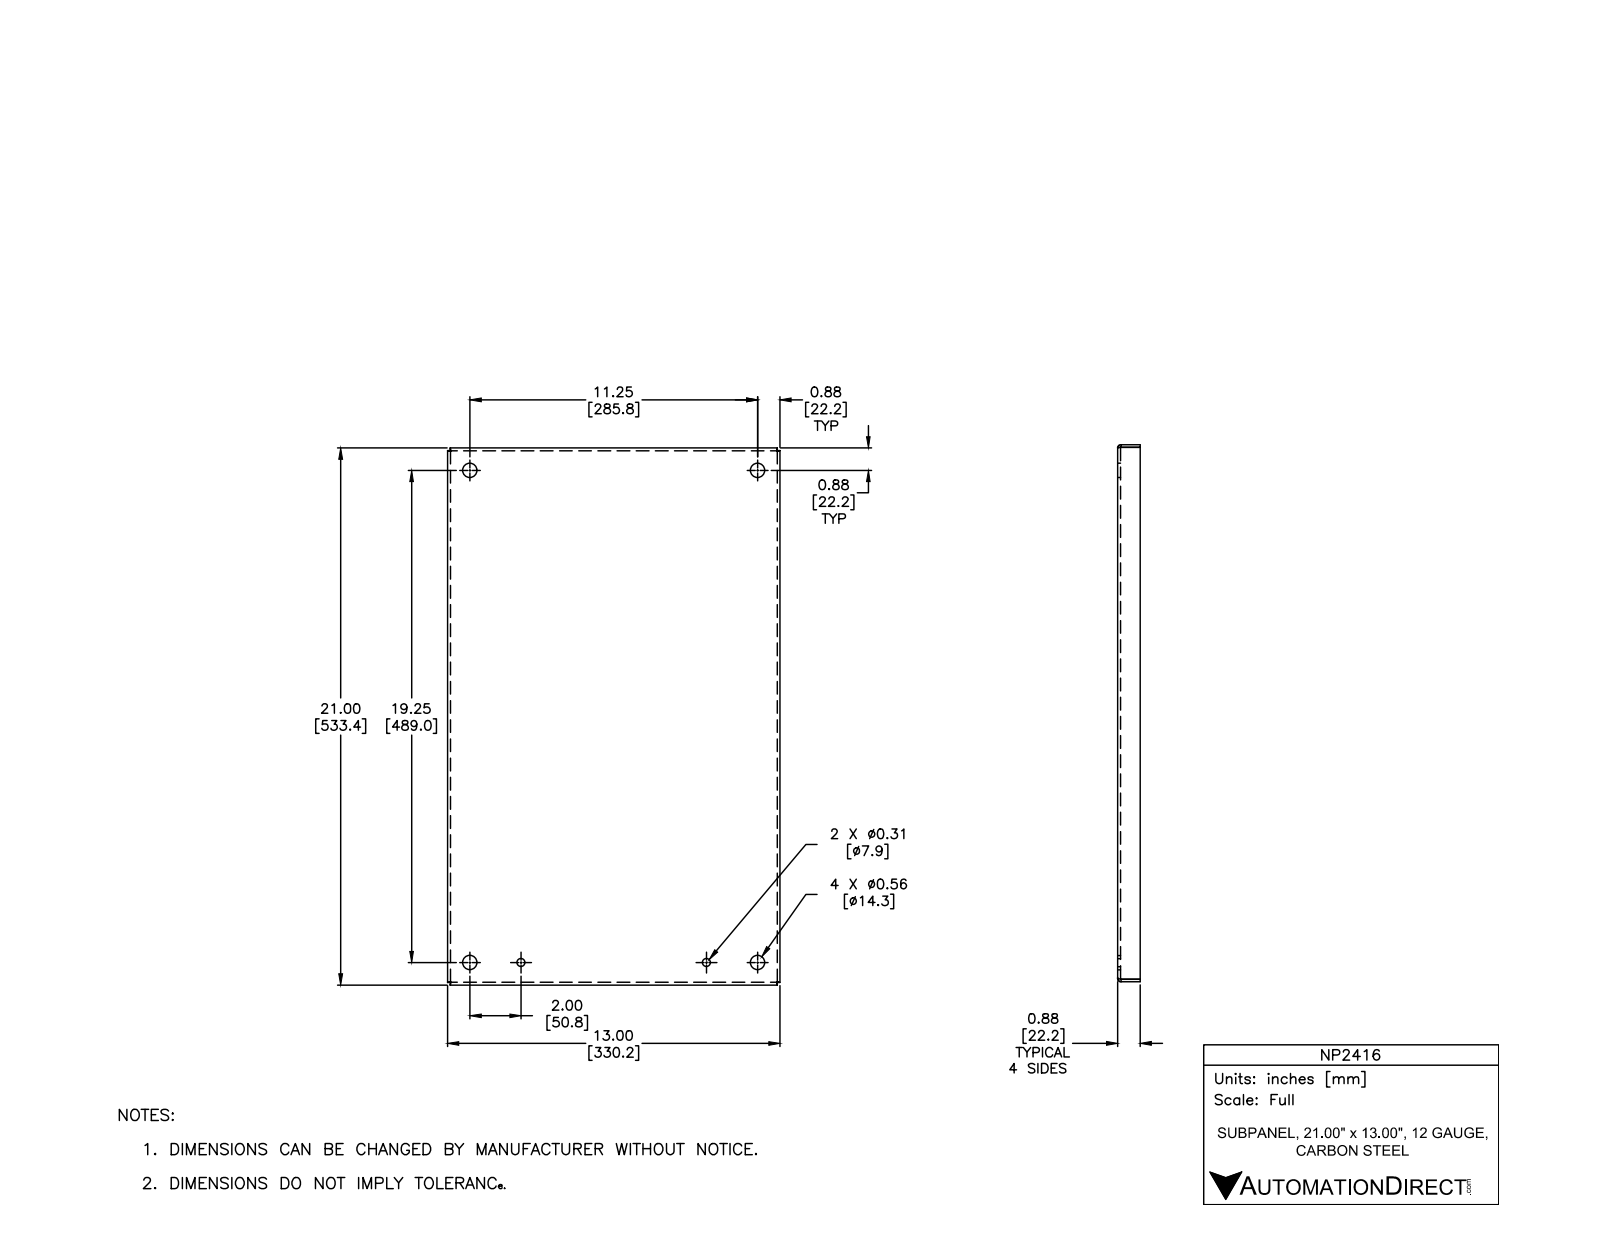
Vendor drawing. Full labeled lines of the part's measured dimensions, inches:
Part name (STEP PRODUCT): NP2416
STEP written by: Autodesk Inventor 2012 (AUTOMOTIVE_DESIGN)
Units: inches
Bodies: 1 solid, 44 faces (22 planar, 14 cylindrical, 8 other)
Overall size (bounding box): 21 × 13 × 0.875
Volume: 30.19 in³ · Surface area: 651.8 in²
Round holes (diameter × count): ⌀0.563 ×4, ⌀0.312 ×2
Partial cylindrical surfaces — rounded edges, fillets, slot ends (radius × count): R0.031 ×4, R0.125 ×4
Main face-to-face distances: 0.094, 12.906, 20.906, 13, 12.813, 21, 20.813, 0.781, 0.875, 0.105
Hole centre spacings: 11.25, 19.25, 19.354, 21.357, 22.296, 2, 2, 7.25
